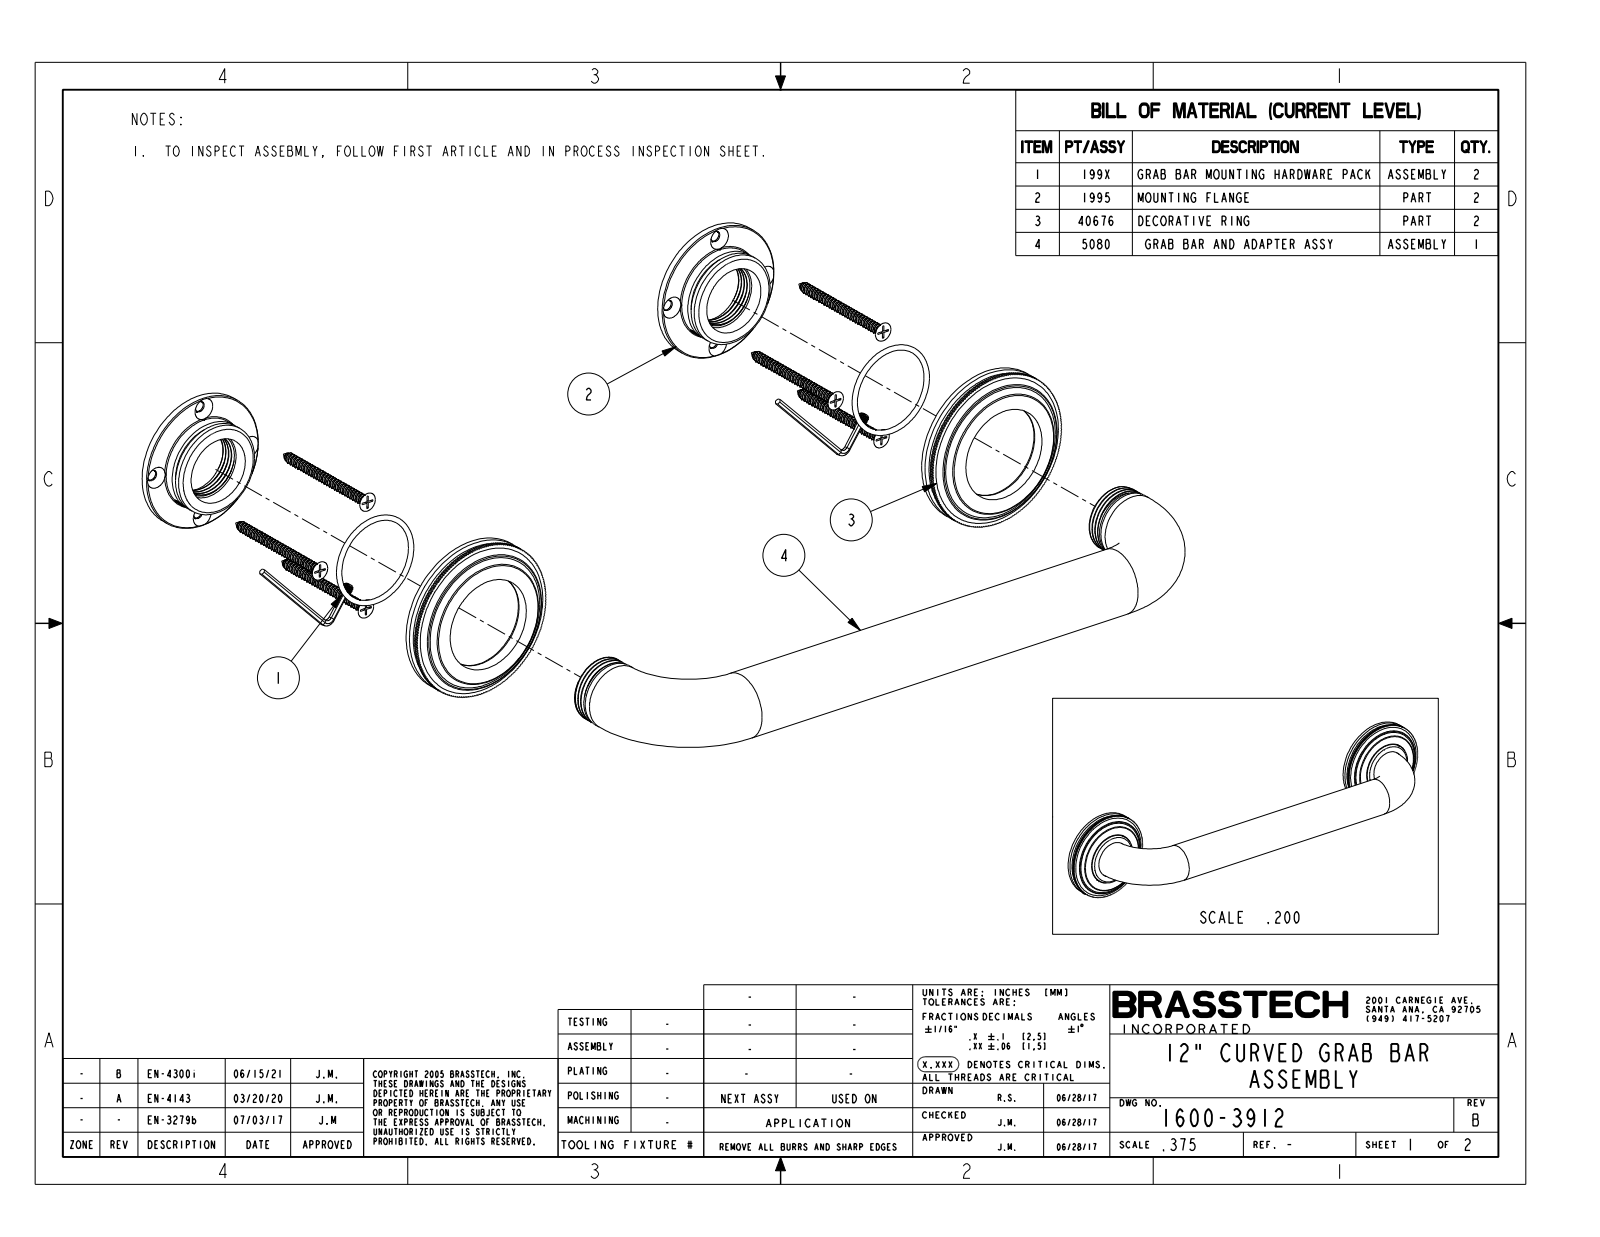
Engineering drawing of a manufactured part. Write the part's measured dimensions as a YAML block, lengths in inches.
part_name: "1600-3912"
step_written_by: "CREO PARAMETRIC BY PTC INC, 2018400 (AUTOMOTIVE_DESIGN)"
units: inches
bodies: {solids: 1, faces: 1134, planar: 732, cylindrical: 374, other: 28}
overall_size: [15, 3, 2.75]
volume: 23.62
surface_area: 89.1
round_bosses_or_shafts:
  - {diameter: 3, count: 2}
  - {diameter: 2.9, count: 2}
  - {diameter: 1.75, count: 2}
  - {diameter: 1.25, count: 1}
face_to_face_distances: [0.525, 0.6, 0.075, 0.325, 0.2, 0.275, 0.1, 0.25, 0.075, 0.275]
